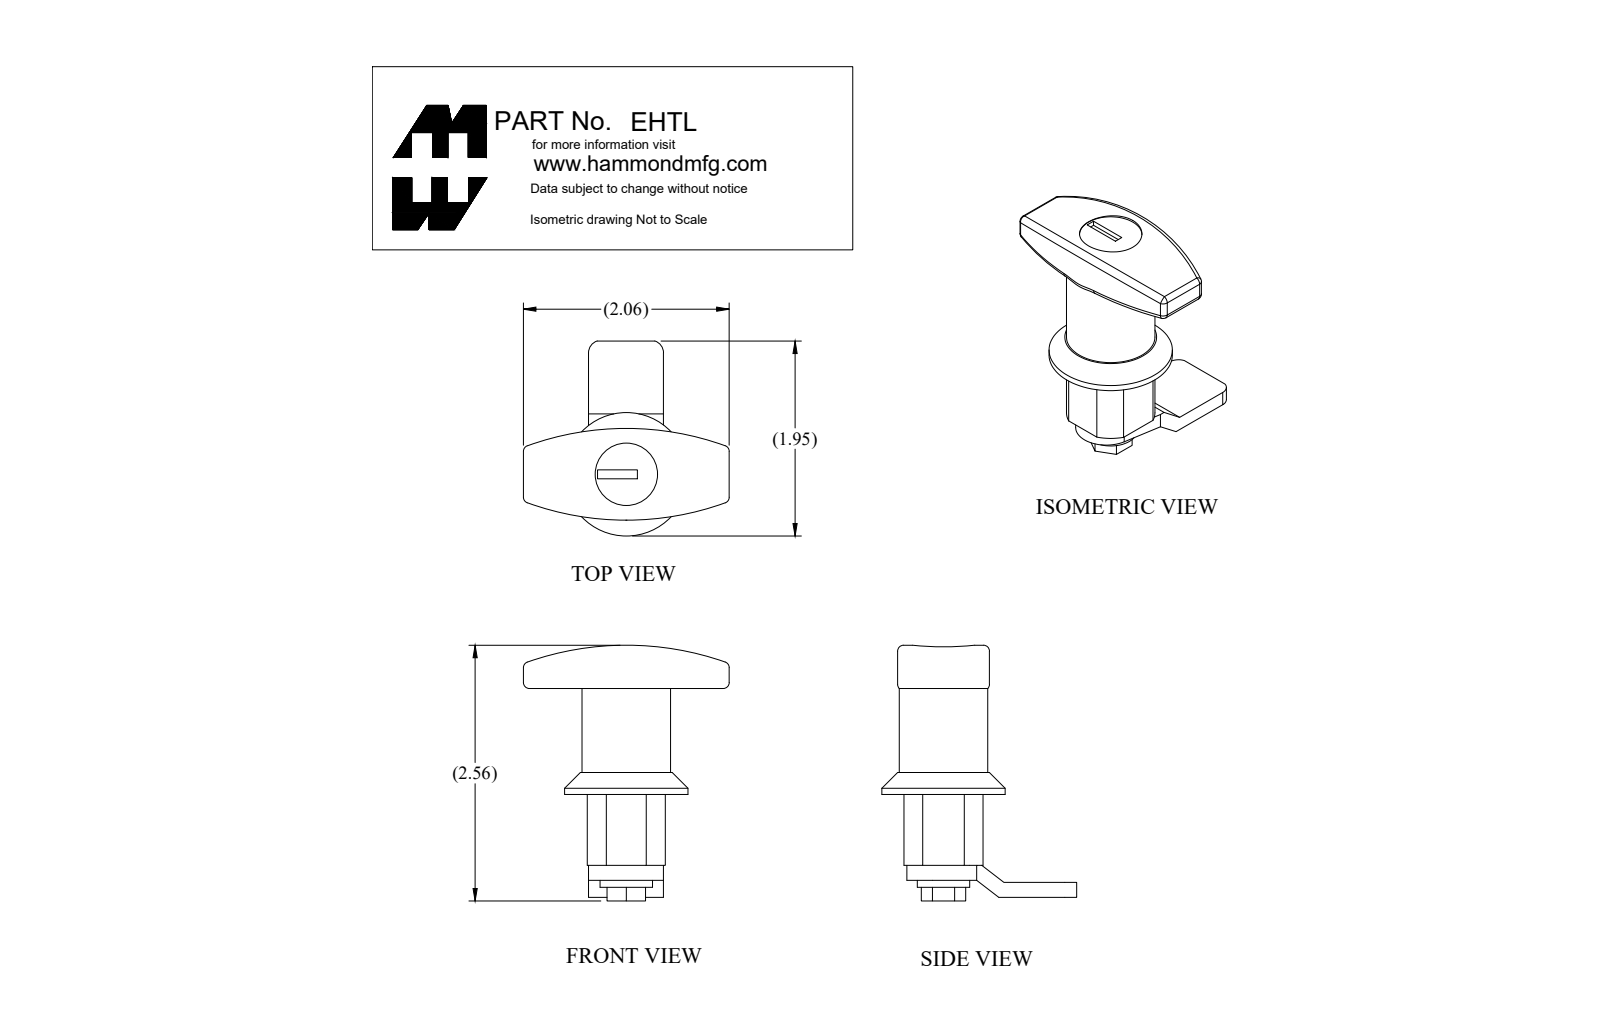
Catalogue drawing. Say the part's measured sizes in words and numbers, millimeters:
The part is named "EHTL_Default". Its 3-D file was written by "SolidWorks 2018 (CONFIG_CONTROL_DESIGN)". It is 3 solids with 98 faces: 48 planar, 32 cylindrical and 18 other. Overall it measures 65 by 52.3 by 49.6 millimeters. Its volume is 32 140 cubic millimeters and its surface area 9 858 square millimeters. Round holes: 1 of diameter 6, 1 of diameter 15.9. Round bosses or shafts: 1 of diameter 31.4, 1 of diameter 22.5, 1 of diameter 13.3, 1 of diameter 5.9. Partial cylindrical surfaces (rounded edges, fillets, slot ends): 8 of radius 1.5, 2 of radius 3.2, 2 of radius 73.9, 1 of radius 7.8, 1 of radius 75.9. The main face-to-face distances are 3.8, 4.3, 44.9, 26.9, 18, 53.1, 26.2, 8.2, 49.3, 22.4.
